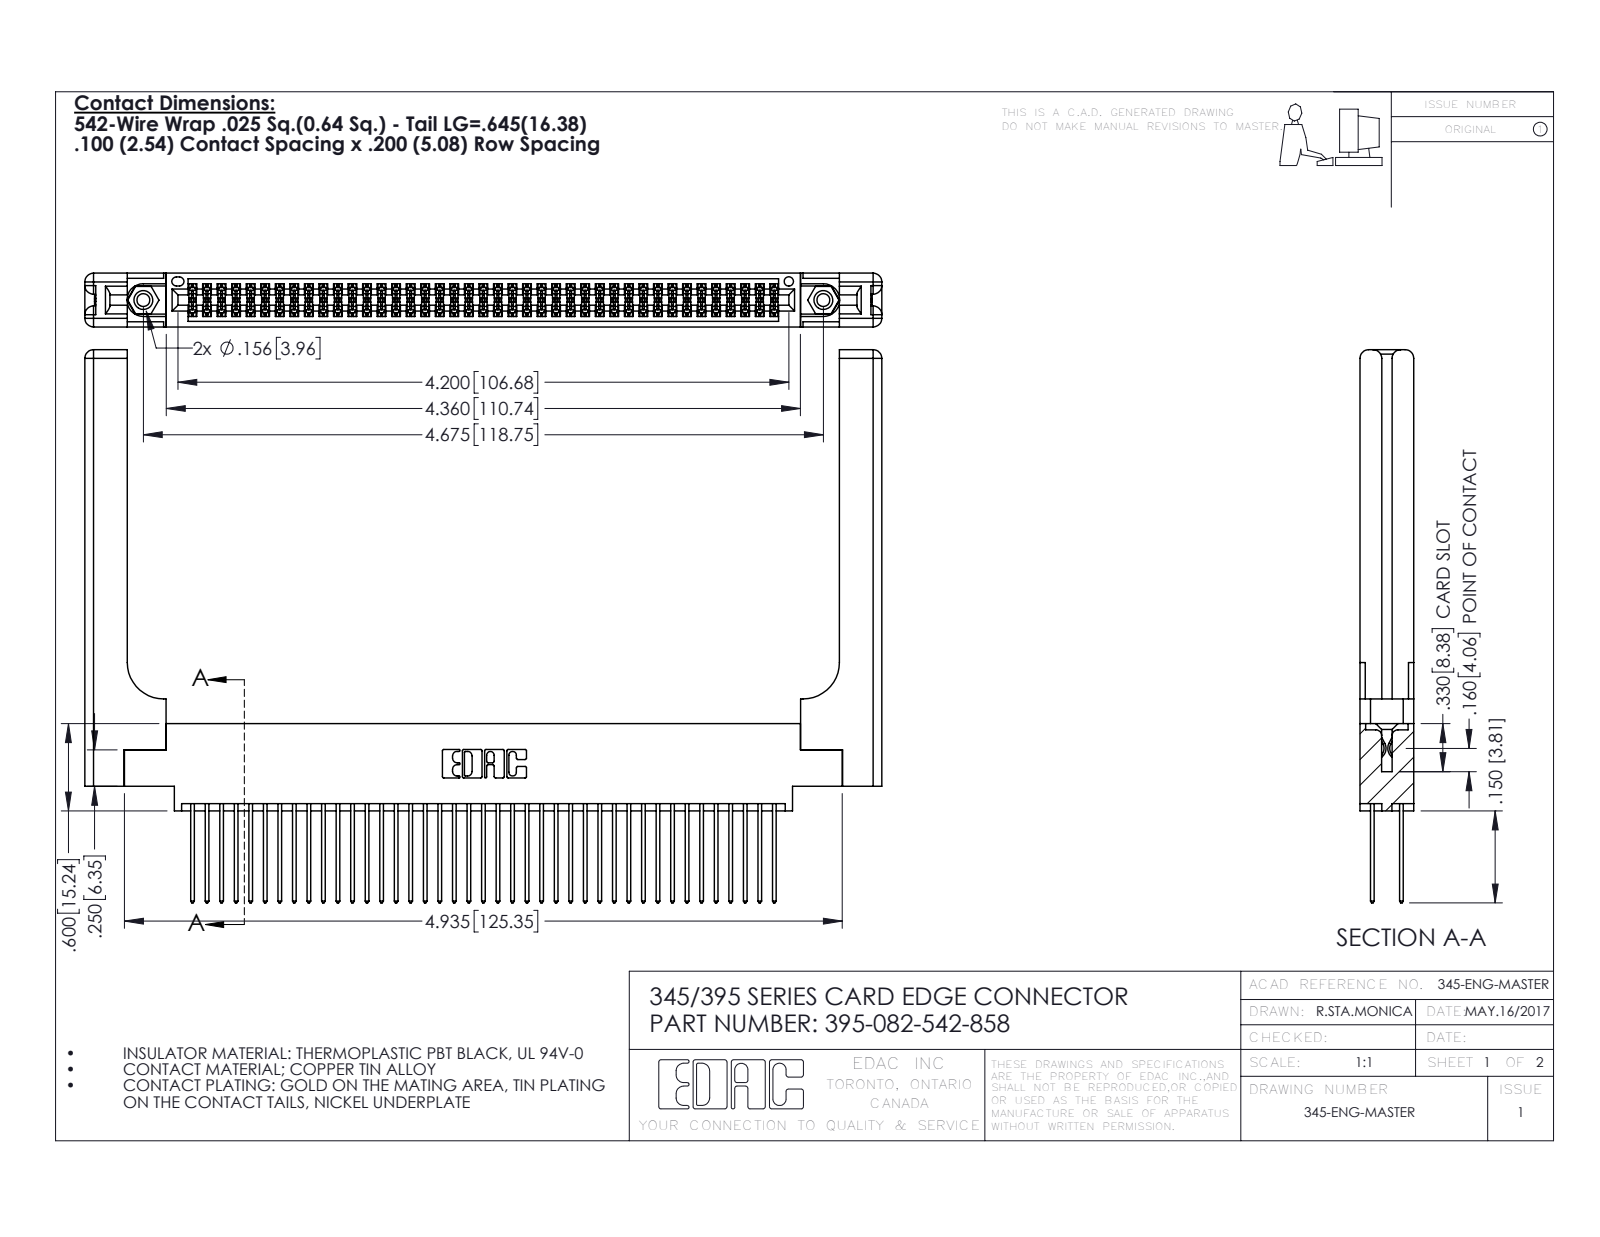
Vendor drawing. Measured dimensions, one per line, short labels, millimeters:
name: 345-292-001_345-293-142; 395-082-542-858; 345-220-058_345-220-058; 345-250-001_345-250-001-102 (+1 more)
written by: SolidWorks 2016 (CONFIG_CONTROL_DESIGN)
unit: mm
bodies: 87 solids, 4486 faces (2938 planar, 1488 cylindrical, 60 other)
size: 139.2 × 96.6 × 9.4
volume: 22 250 mm³; area: 27 340 mm²
holes: 2× ⌀2.3, 2× ⌀3.2, 2× ⌀4, 1× ⌀1.6
bosses: 2× ⌀3.9
rounds: 123× R0.2, 82× R0.3, 22× R0.3, 16× R1.5, 6× R0.2, 6× R0.8, 3× R0.7, 2× R0.4
face distances: 1.8, 7.6, 9.4, 2.5, 6.9, 0.6, 5.1, 5.7, 4.4, 3.8
hole spacings: 6.9, 112.8, 118.7
